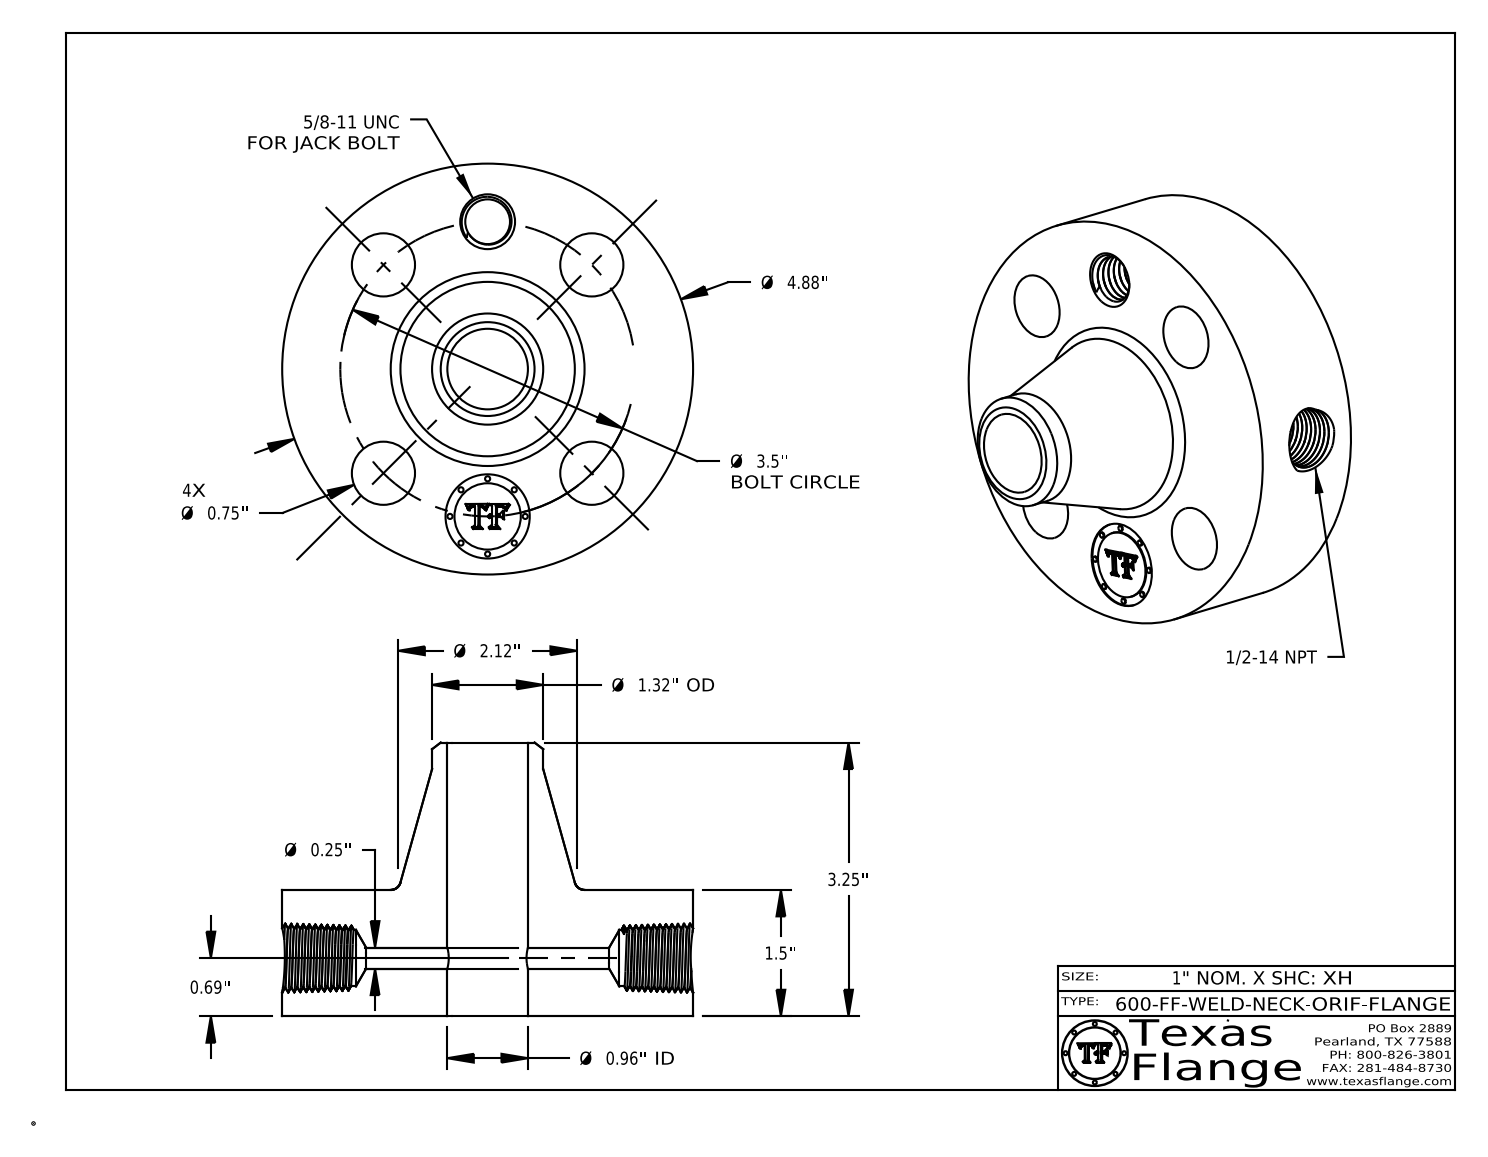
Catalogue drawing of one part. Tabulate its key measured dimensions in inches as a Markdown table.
| quantity | value |
| --- | --- |
| part name | 600-FF-WELD-NECK |
| STEP written by | CATIA V5 STEP AP214 (AUTOMOTIVE_DESIGN) |
| units | inches |
| bodies | 1 solid, 761 faces (368 planar, 85 cylindrical, 308 other) |
| overall size | 4.88 × 4.88 × 3.25 |
| volume | 25.61 in³ |
| surface area | 97.98 in² |
| round holes (diameter × count) | 0.75 × 4, 0.25 × 1, 0.531 × 1, 0.672 × 1, 0.957 × 1, 1 × 1 |
| round bosses / shafts (diameter × count) | 0.061 × 8, 4.88 × 1, 1.32 × 1, 0.788 × 1 |
| main face-to-face distances | 1.5, 1.485, 0.015, 3.25, 1.765, 1.75, 0.298, 0.293, 0.054, 0.248 |
| hole center spacings | 1.75, 1.339, 2.475, 3.233, 3.5 |
